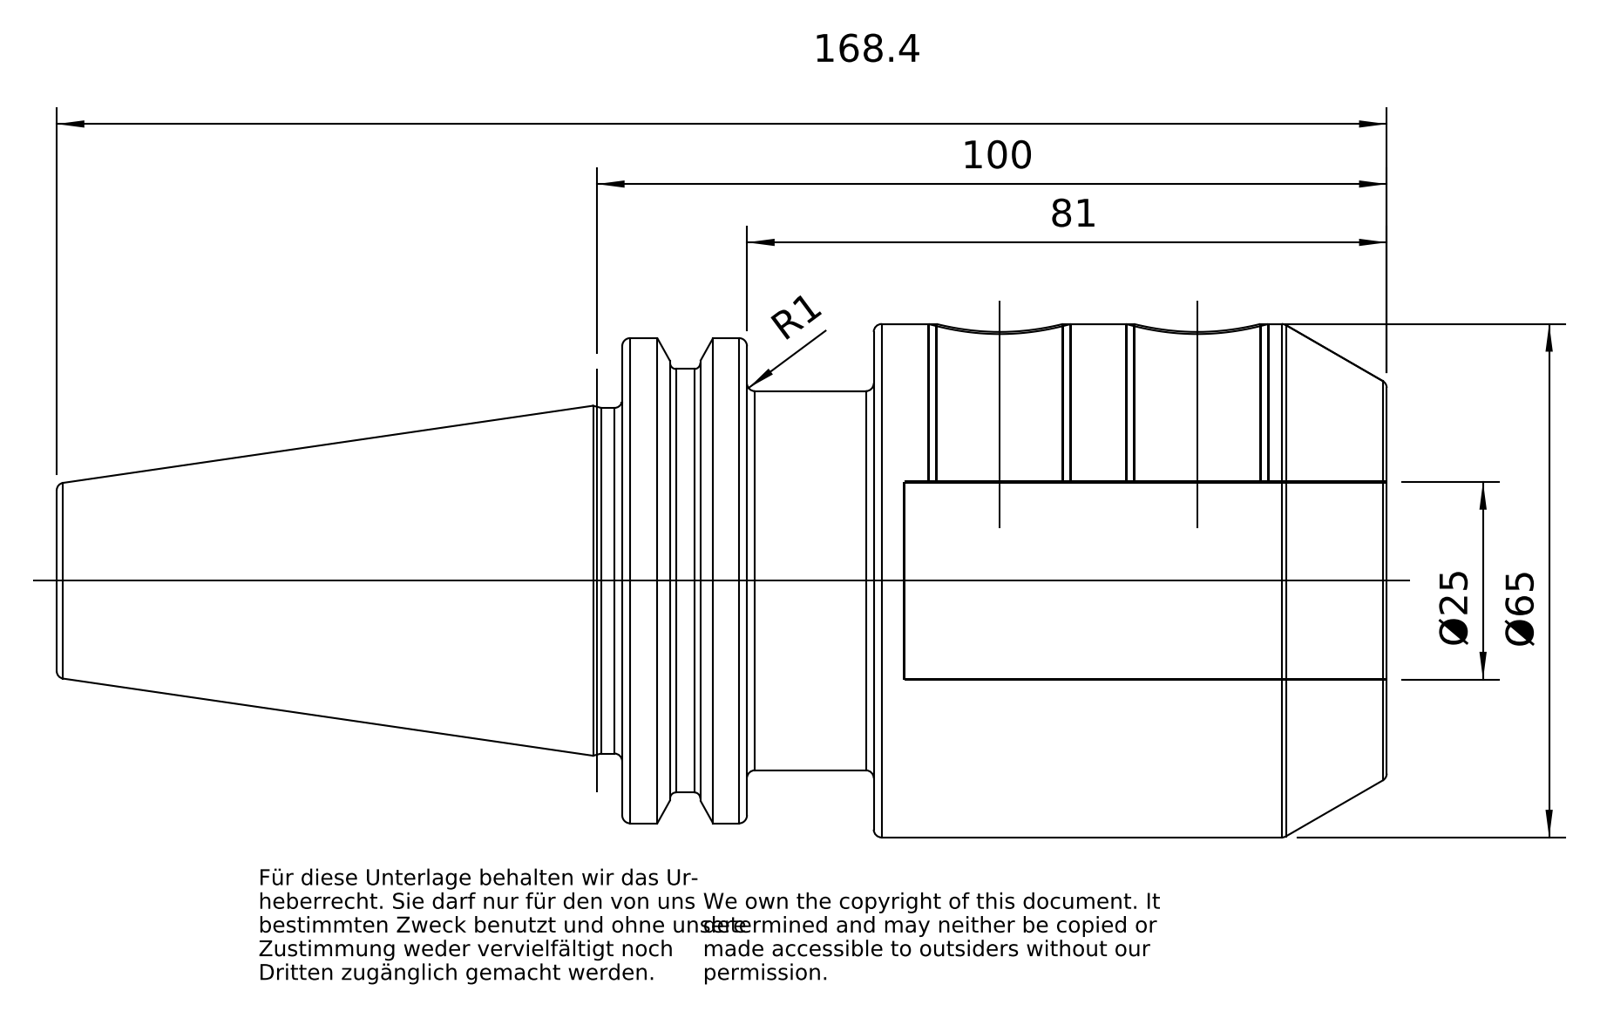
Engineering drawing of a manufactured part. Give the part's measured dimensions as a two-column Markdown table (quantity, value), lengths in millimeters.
| quantity | value |
| --- | --- |
| part name | 40-300-25 |
| STEP written by | PRO/ENGINEER BY PARAMETRIC TECHNOLOGY CORPORATION, 2010430 (CONFIG_CONTROL_DESIGN) |
| units | millimeters |
| bodies | 1 solid, 111 faces (24 planar, 34 cylindrical, 53 other) |
| overall size | 168.25 × 65 × 65 |
| volume | 302 808 mm³ |
| surface area | 45 629 mm² |
| round holes (diameter × count) | 16 × 2, 18 × 2, 13.84 × 1, 17.01 × 1, 17.5 × 1, 25 × 1 |
| round bosses / shafts (diameter × count) | 65 × 1, 48 × 1, 43.75 × 1, 16.01 × 1 |
| partial cylindrical surfaces (radius × count) | 1.35 × 1, 28 × 1, 31.76 × 1 |
| main face-to-face distances | 64.95, 31.85, 96.8, 15.85, 16, 80.95, 35.7, 19.85, 3.85, 61.1 |
| hole center spacings | 25 |
